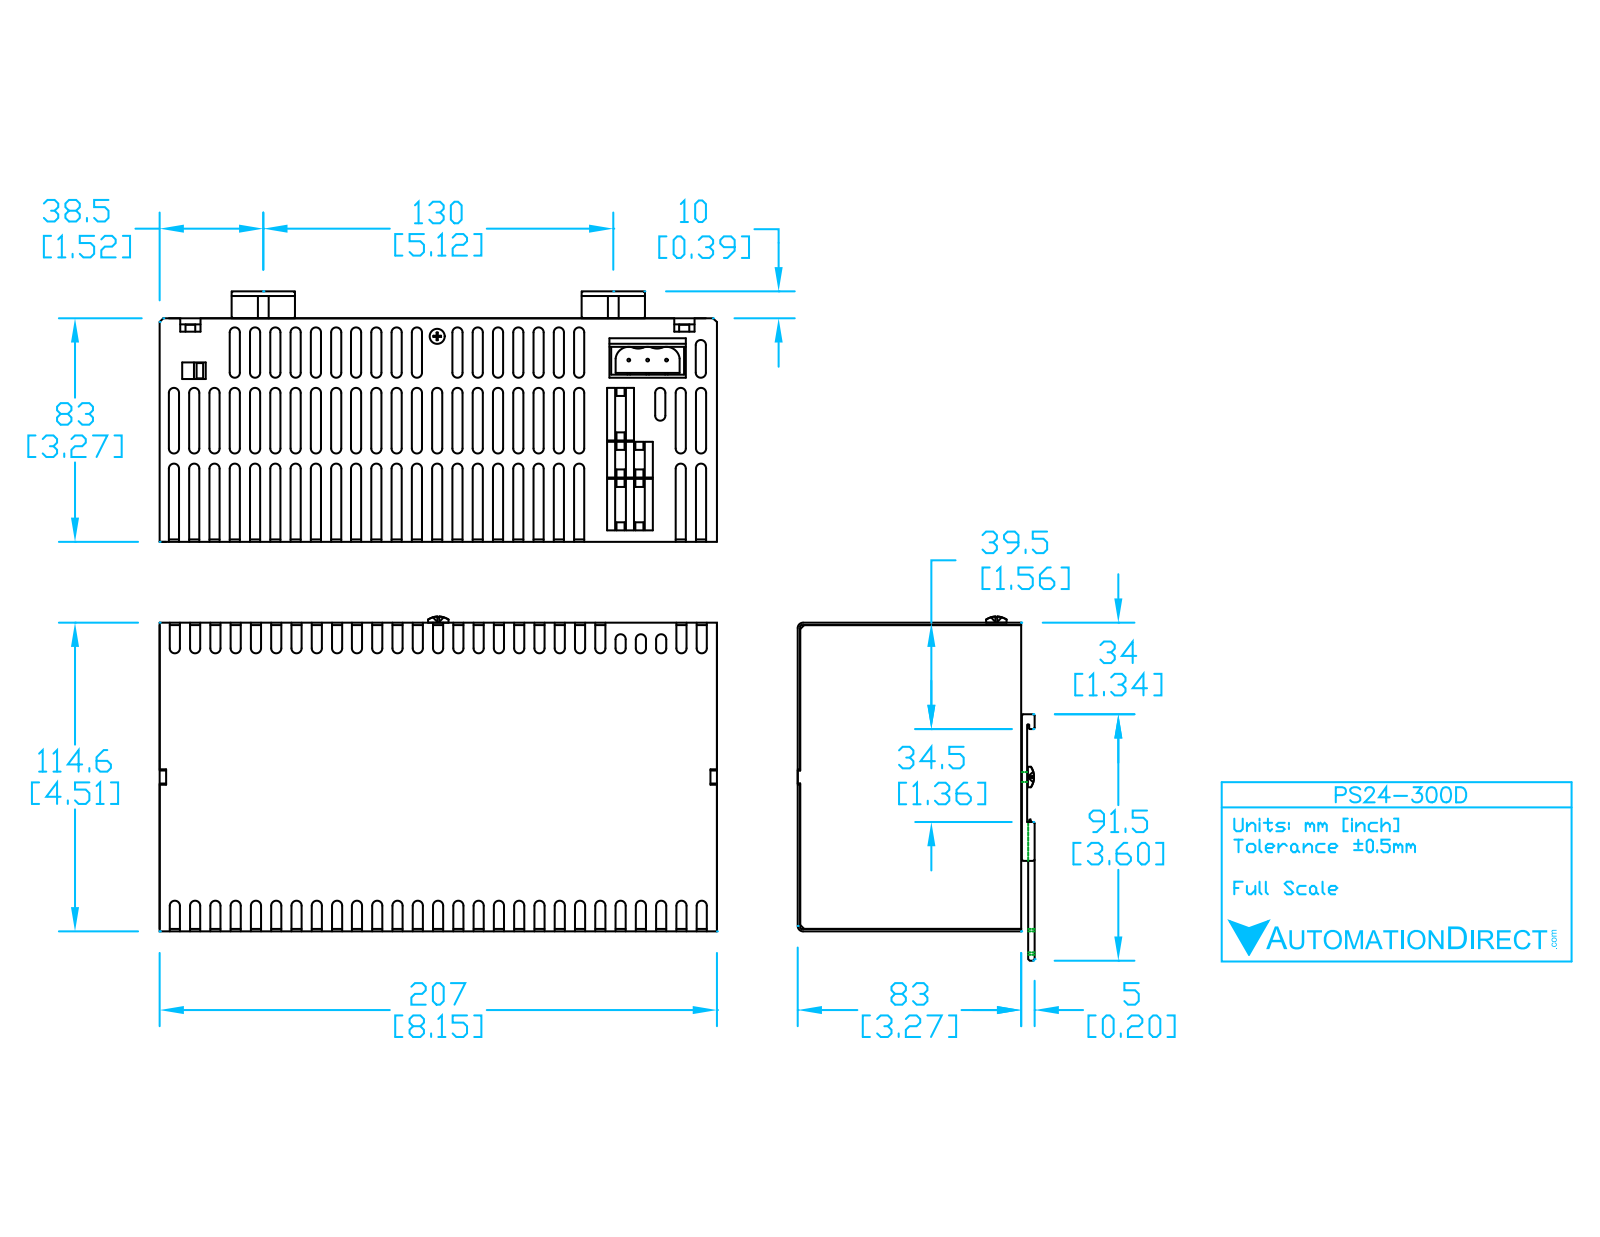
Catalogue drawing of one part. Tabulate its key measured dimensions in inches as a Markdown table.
| quantity | value |
| --- | --- |
| part name | PS24-300D |
| STEP written by | SolidWorks 2011 (CONFIG_CONTROL_DESIGN) |
| units | inches |
| bodies | 1 solid, 1456 faces (864 planar, 506 cylindrical, 86 other) |
| overall size | 8.246 × 5.324 × 3.734 |
| volume | 72.63 in³ |
| surface area | 287.6 in² |
| round holes (diameter × count) | 0.15 × 7 |
| round bosses / shafts (diameter × count) | 0.265 × 2, 0.21 × 2, 0.3 × 1, 0.212 × 1 |
| partial cylindrical surfaces (radius × count) | 0.076 × 169, 0.06 × 4, 0.015 × 2, 0.02 × 2, 0.05 × 2, 0.1 × 2 |
| main face-to-face distances | 0.04, 4.47, 2.495, 3.269, 3.5, 1.005, 1.01, 3.506, 4.51, 3.46 |
| hole center spacings | 0.2, 0.3, 0.4, 0.6, 7.648, 7.195, 7.344, 7.419 |
